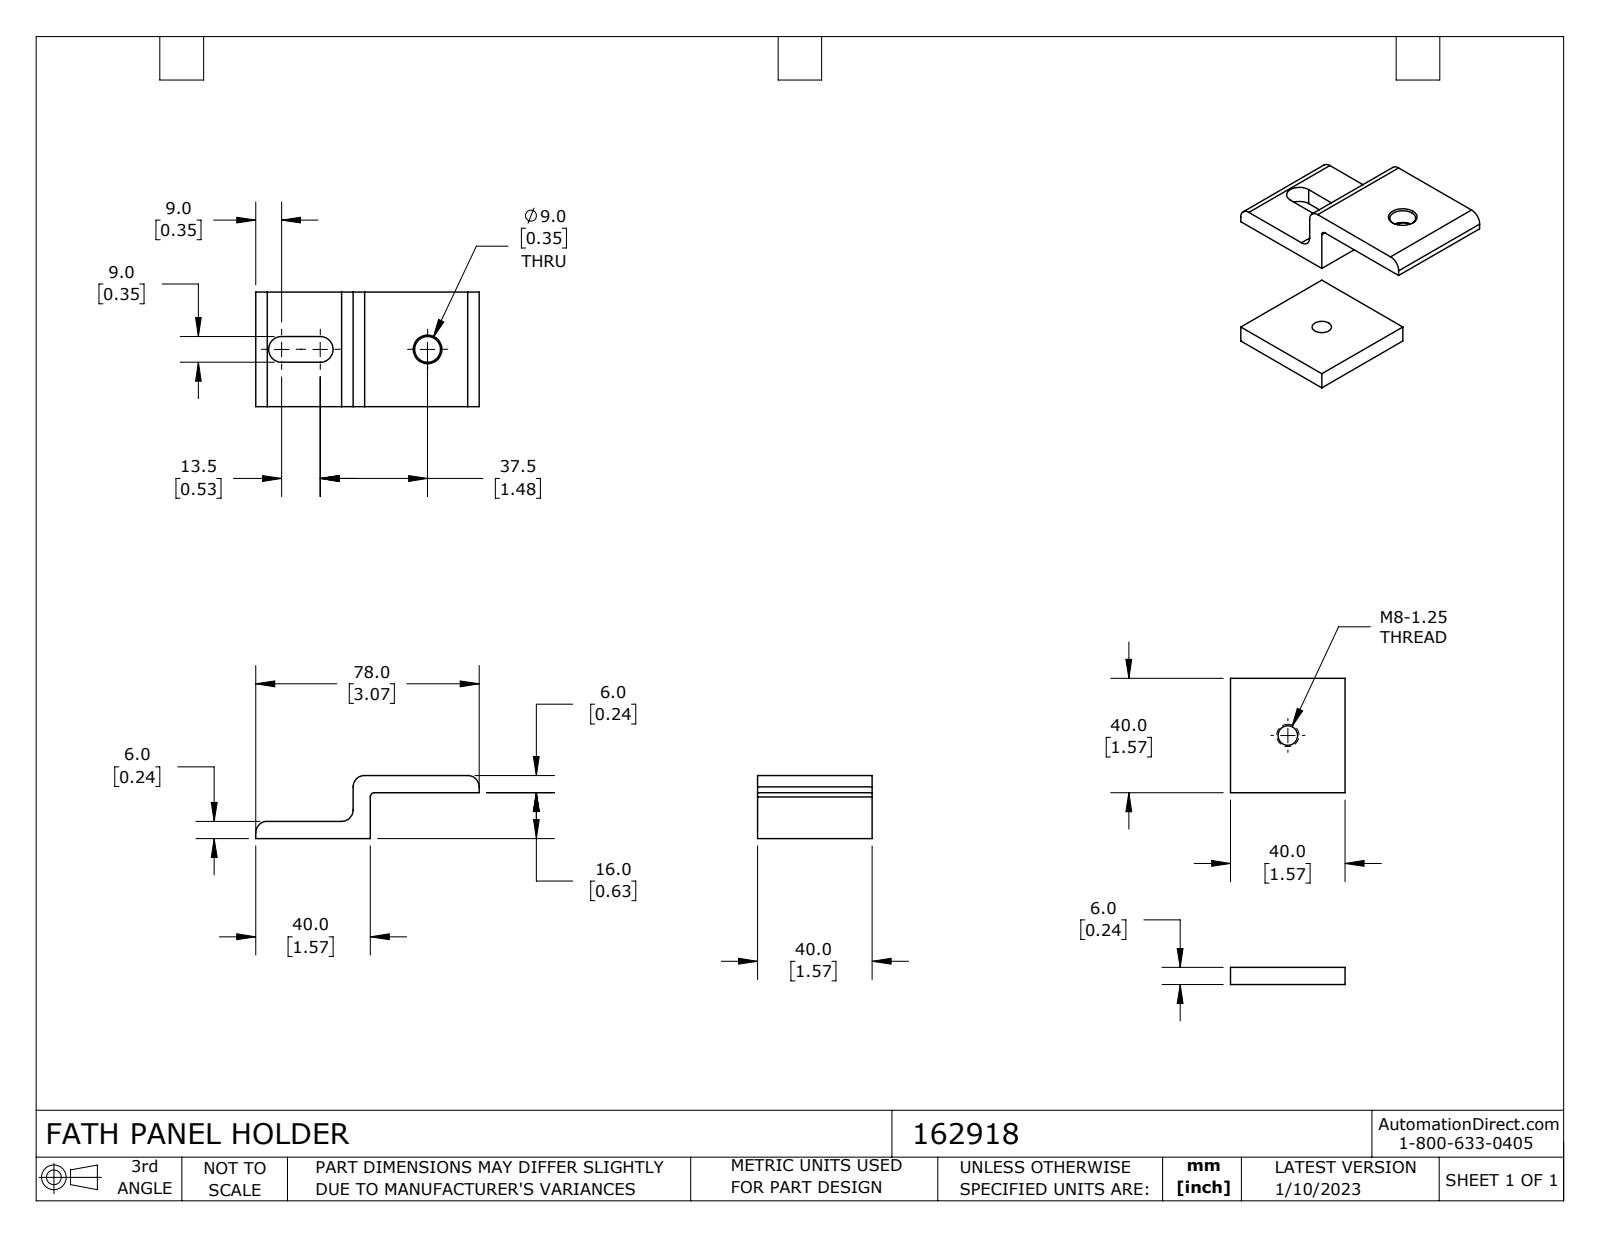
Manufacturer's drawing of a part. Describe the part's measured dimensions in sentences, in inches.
The part is named "162918". Its 3-D file was written by "SolidWorks 2021 (CONFIG_CONTROL_DESIGN)". It is 1 solid with 25 faces: 12 planar, 9 cylindrical and 4 other. Overall it measures 3.071 by 1.575 by 0.866 inches. Its volume is 1.27 cubic inches and its surface area 13.64 square inches. Round holes: 1 of diameter 0.354. Partial cylindrical surfaces (rounded edges, fillets, slot ends): 4 of radius 0.157, 2 of radius 0.177, 1 of radius 0.059. The main face-to-face distances are 0.236, 0.63, 0.866, 0.394, 1.575, 0.61, 0.965, 0.354, 1.339, 1.496.
